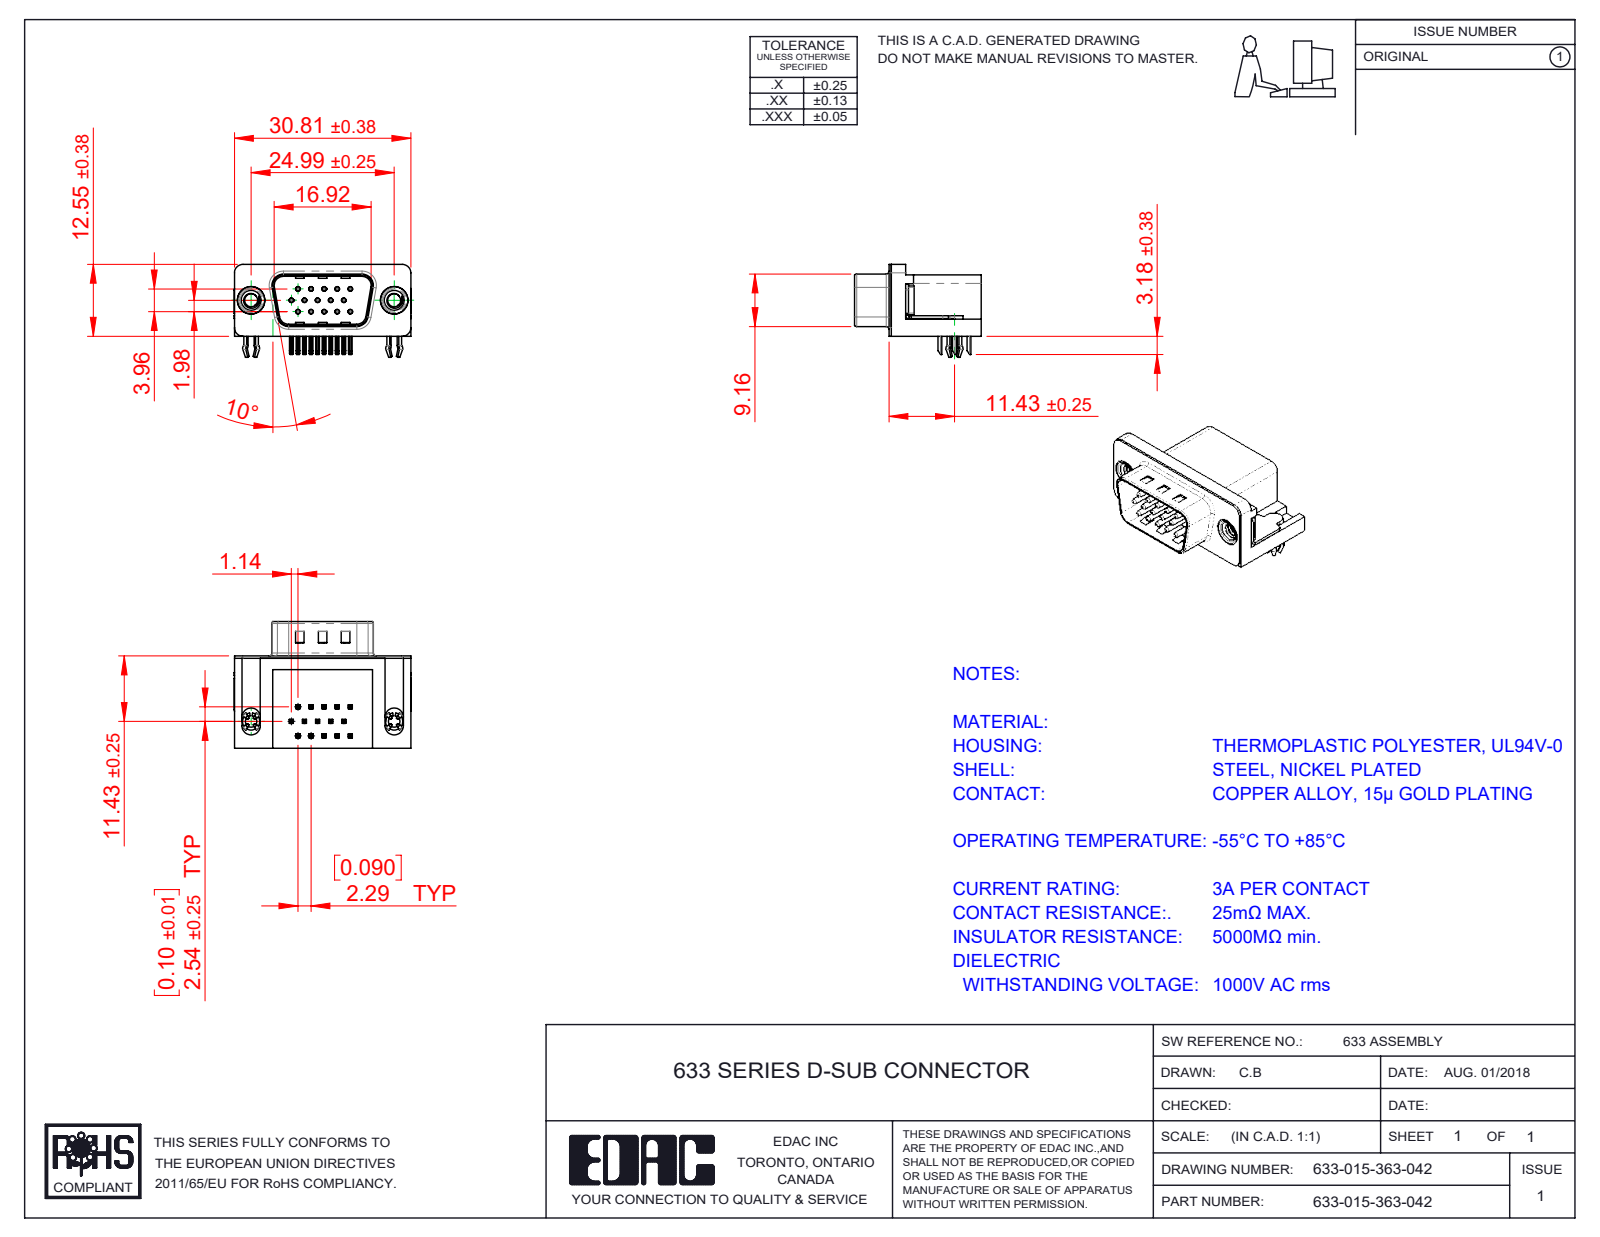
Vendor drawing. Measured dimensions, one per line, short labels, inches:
name: 633 Housing_15 Contact; 633 Shell_15 Contact; 633 4 Prong Board Lock; 633 Contact Bottom (+4 more)
written by: SolidWorks 2016 (CONFIG_CONTROL_DESIGN)
unit: in
bodies: 21 solids, 1563 faces (903 planar, 449 cylindrical, 211 other)
size: 1.216 × 0.87 × 0.64
volume: 0.249 in³; area: 8.523 in²
holes: 15× ⌀0.014, 15× ⌀0.031, 2× ⌀0.079, 2× ⌀0.089, 2× ⌀0.157, 2× ⌀0.189, 2× ⌀0.197
bosses: 15× ⌀0.03, 2× ⌀0.193, 2× ⌀0.187, 2× ⌀0.154, 2× ⌀0.118
rounds: 72× R0.01, 30× R0.005, 16× R0.039, 9× R0.02, 8× R0.063, 7× R0.059, 4× R0.035, 4× R0.079
face distances: 0.016, 0.407, 0.618, 0.114, 0.264, 0.634, 0.098, 0.02, 0.014, 0.421
hole spacings: 0.156, 0.09, 0.18, 0.09, 0.238, 0.27, 0.312, 0.238
